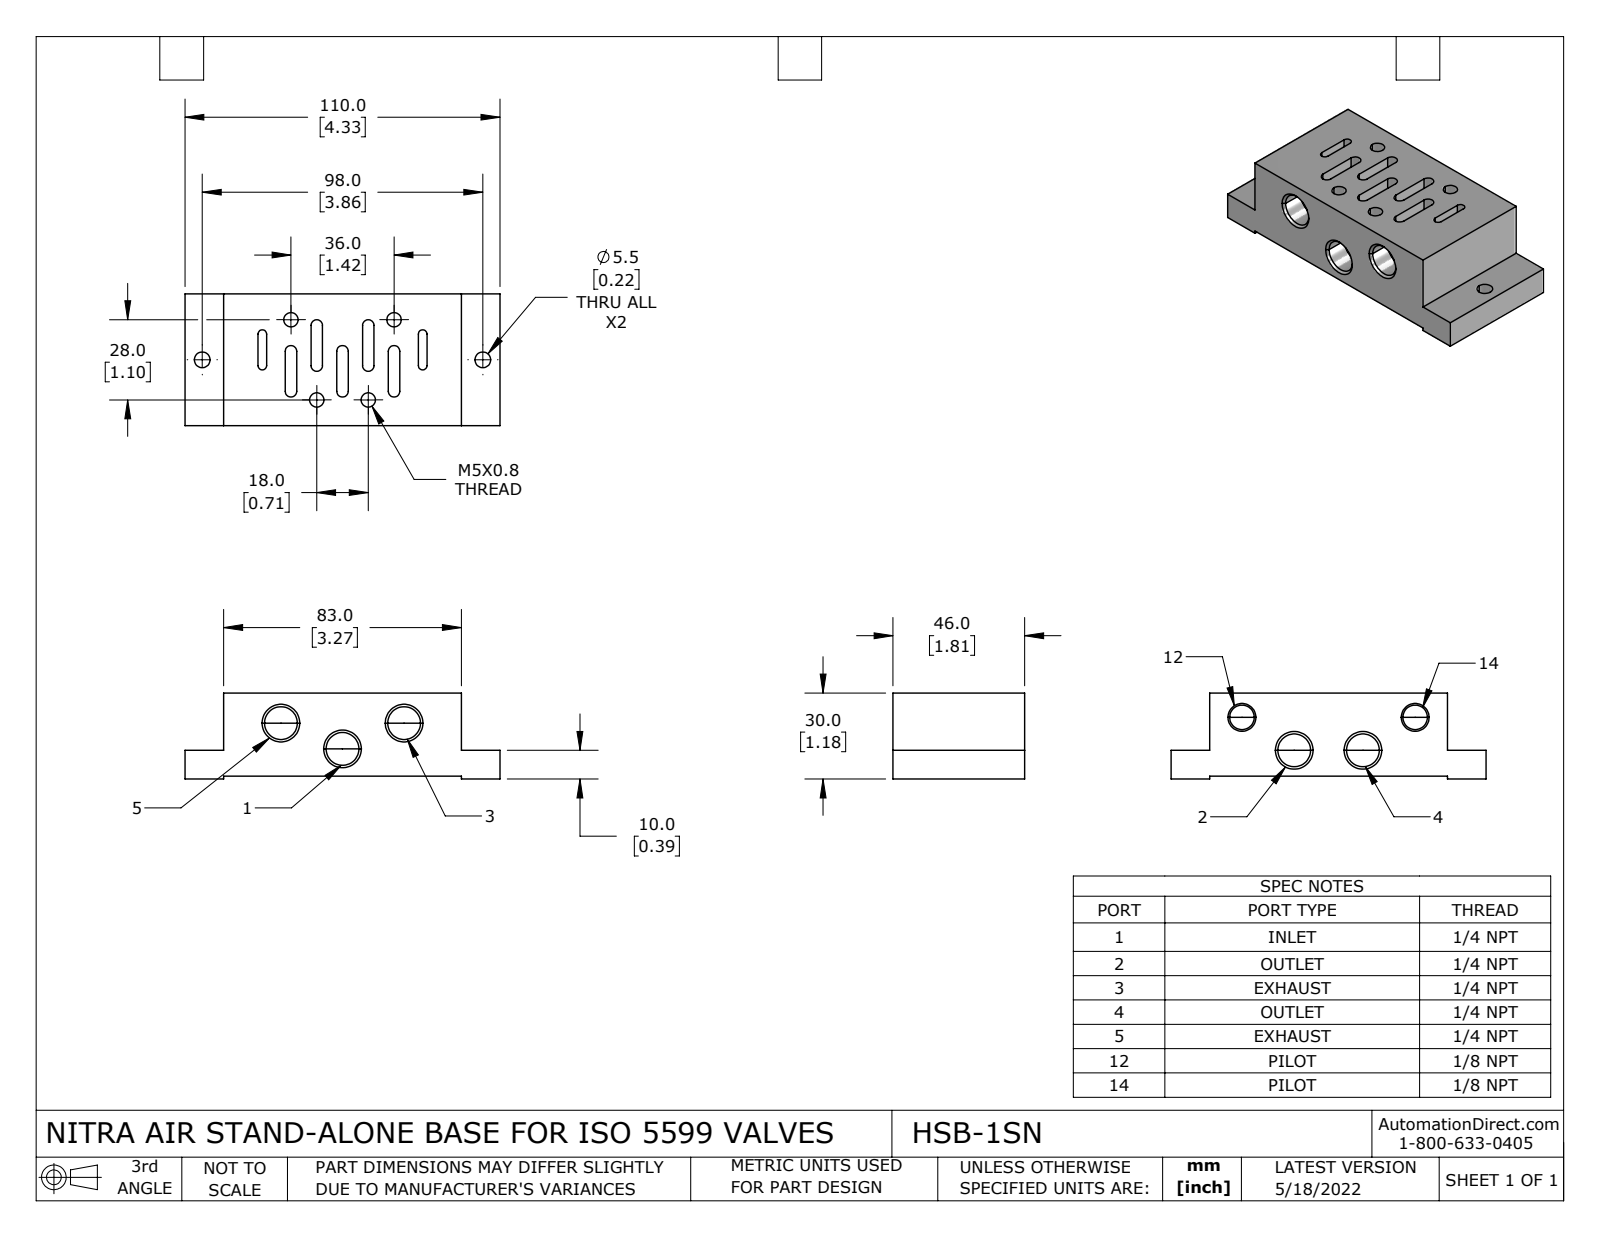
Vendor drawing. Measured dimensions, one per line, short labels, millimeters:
name: HSB-1SN
written by: SolidWorks 2021 (CONFIG_CONTROL_DESIGN)
unit: mm
bodies: 1 solid, 107 faces (39 planar, 40 cylindrical, 28 other)
size: 110 × 46 × 30
volume: 112 739 mm³; area: 22 817 mm²
holes: 5× ⌀11.45, 4× ⌀5, 2× ⌀5.5, 2× ⌀8.57
rounds: 10× R2, 4× R1.5
face distances: 29, 46, 9, 1, 10, 30, 20, 13.5, 83, 96.5
hole spacings: 8.98, 12.01, 13.44, 21.57, 23.31, 29.41, 32.19, 34.01
